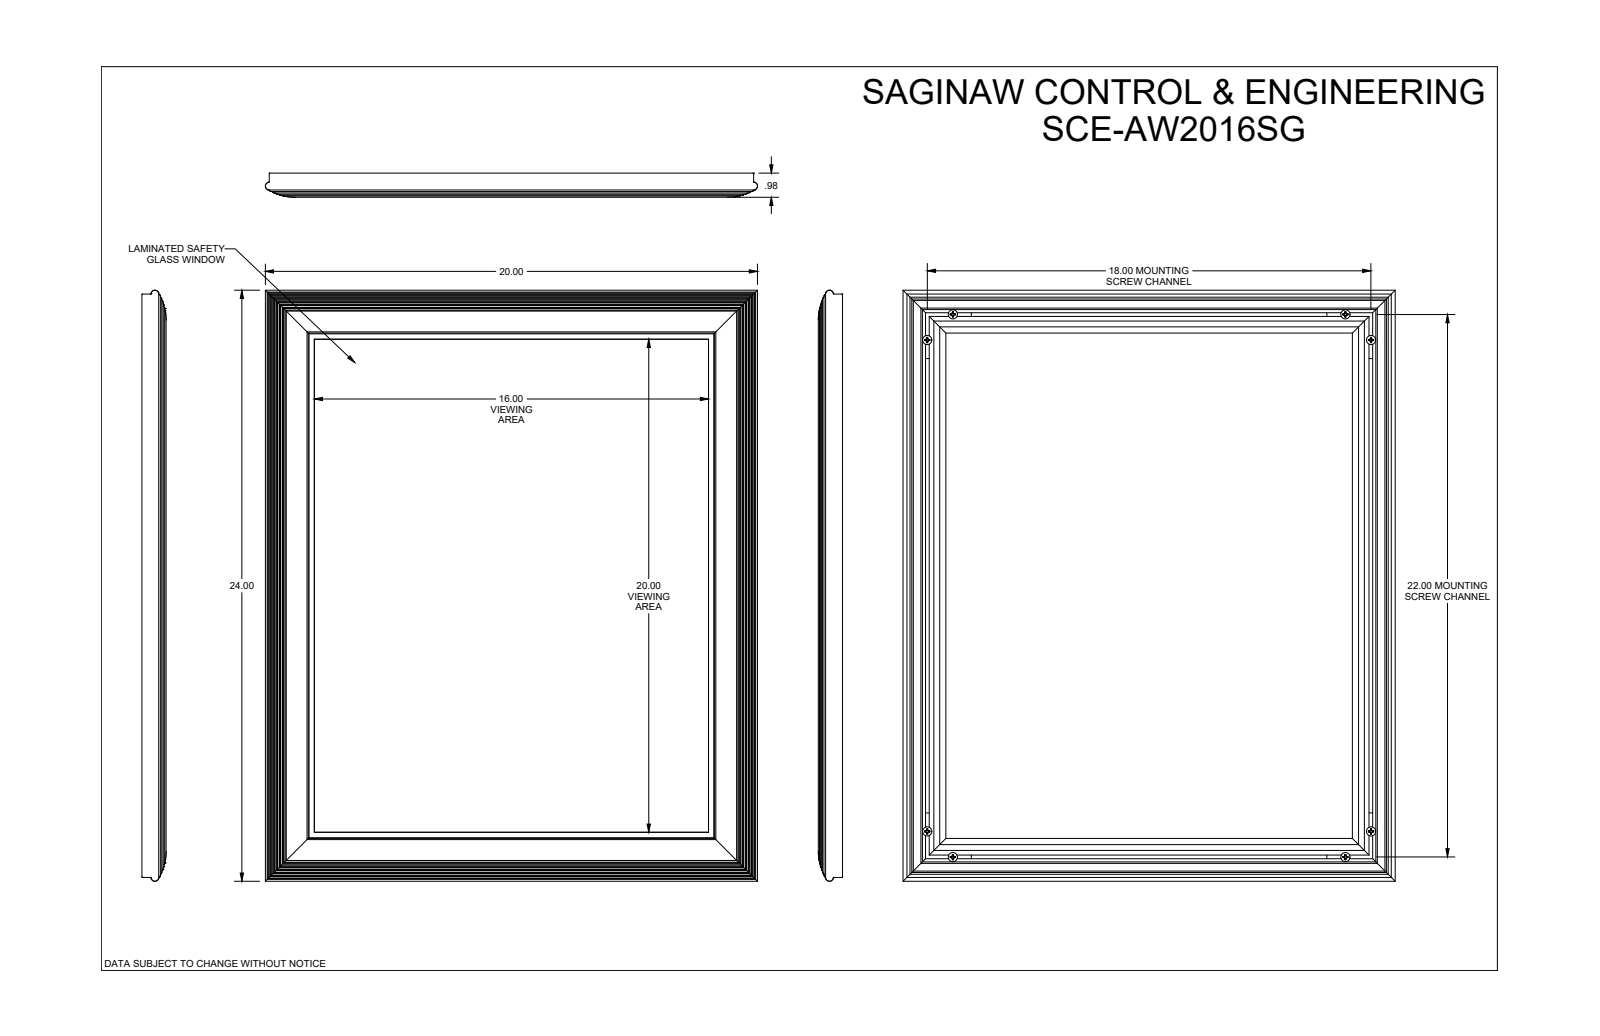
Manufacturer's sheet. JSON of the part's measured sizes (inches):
{"part_name": "SCE-AW2016SG", "step_written_by": "SolidWorks 2019 (CONFIG_CONTROL_DESIGN)", "units": "inches", "bodies": {"solids": 25, "faces": 1202, "planar": 454, "cylindrical": 308, "other": 440}, "overall_size": [23.976, 19.976, 0.98], "volume_in3": 129.8, "surface_area_in2": 1893, "round_holes": [[0.148, 8], [0.165, 4]], "round_bosses_or_shafts": [[0.19, 8], [0.122, 8]], "partial_cylinders_radius": [[0.02, 156], [0.059, 24], [0.01, 16], [0.03, 12], [0.016, 4], [0.02, 4], [0.06, 4], [0.157, 4]], "face_to_face_distances": [0.236, 0.06, 0.065, 0.075, 0.216, 0.02, 0.125, 1.52, 0.563, 0.313], "hole_center_spacings": [1.474, 17.005, 21, 26.981, 15.931, 18.016, 19.931, 22.016]}
